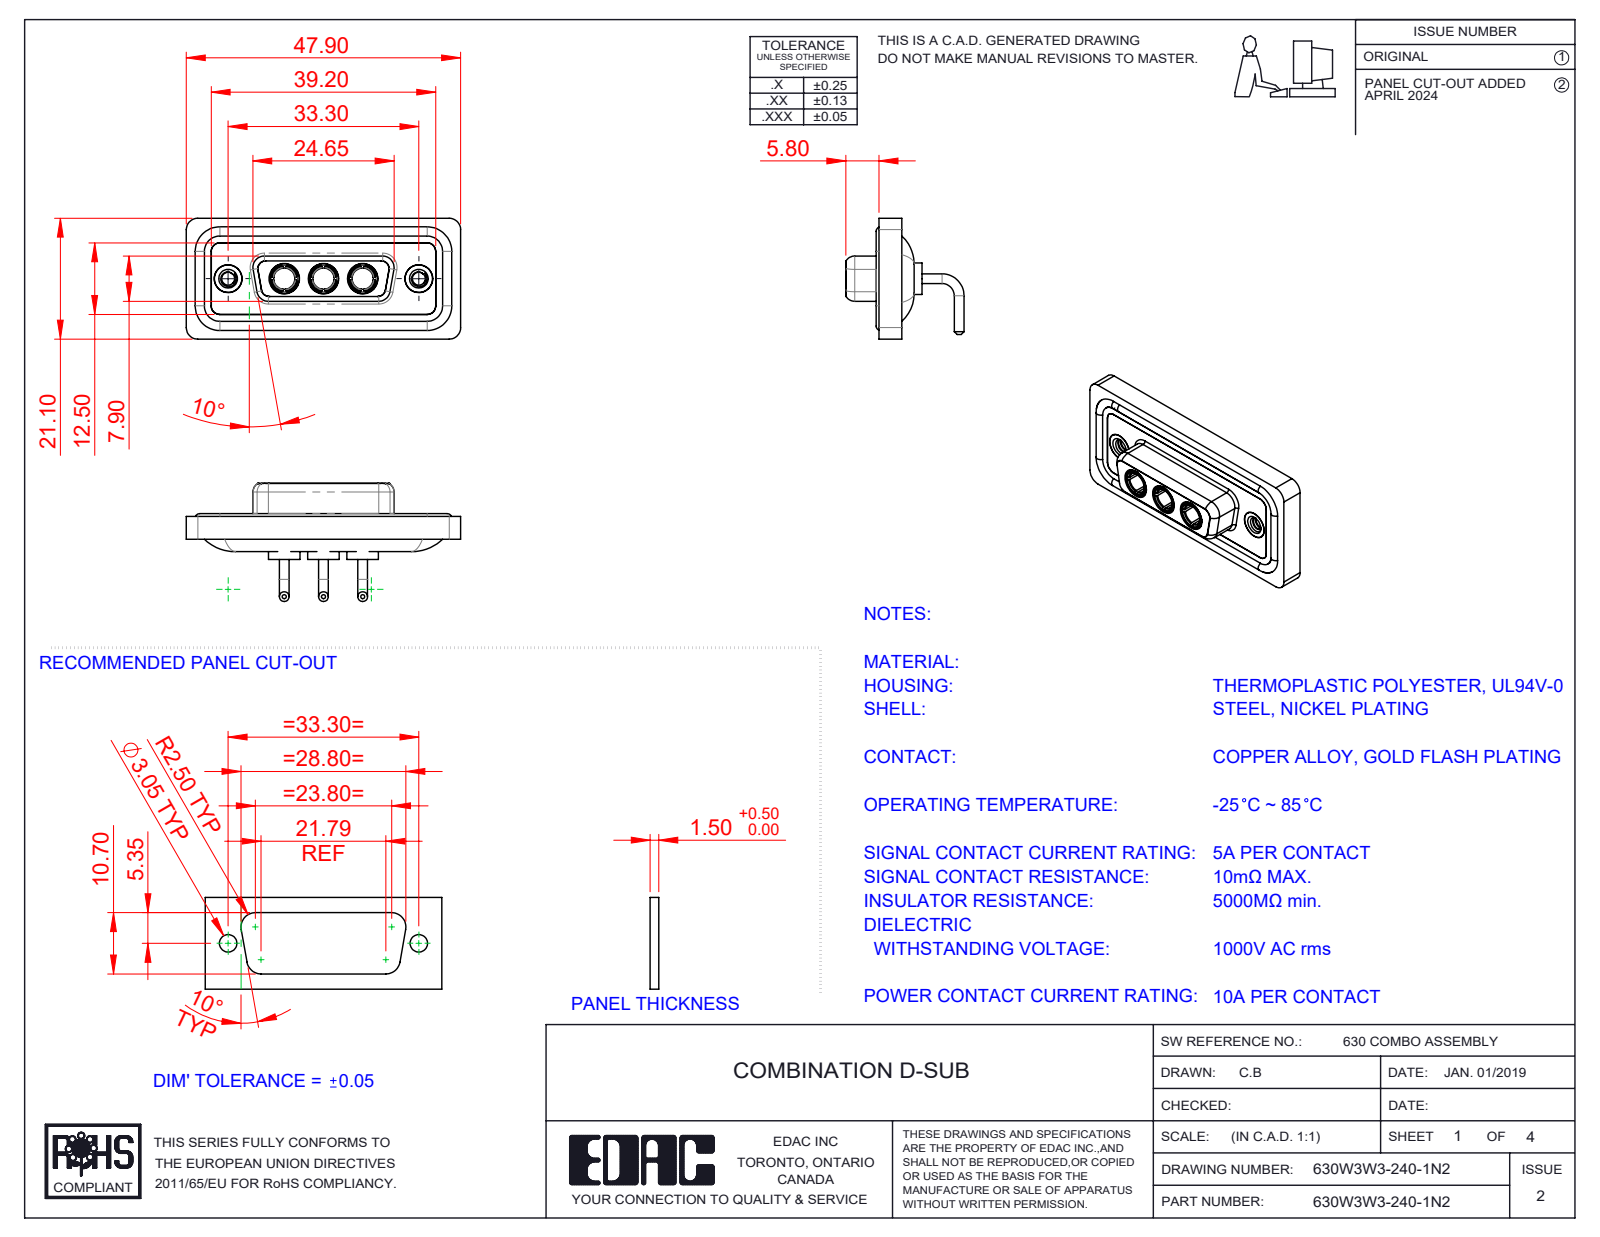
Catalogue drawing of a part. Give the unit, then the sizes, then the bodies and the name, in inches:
Units: inches
Overall size (bounding box): 1.886 × 0.831 × 0.813
Round holes (diameter × count): ⌀0.191 ×5, ⌀0.146 ×3, ⌀0.209 ×3, ⌀0.089 ×2, ⌀0.157 ×2, ⌀0.159 ×2, ⌀0.197 ×2
Round bosses / shafts (diameter × count): ⌀0.067 ×6, ⌀0.063 ×4, ⌀0.217 ×3, ⌀0.205 ×3, ⌀0.195 ×3, ⌀0.187 ×3, ⌀0.148 ×3, ⌀0.195 ×2
Partial cylindrical surfaces — rounded edges, fillets, slot ends (radius × count): R0.079 ×20, R0.059 ×18, R0.053 ×12, R0.063 ×8, R0.01 ×4, R0.02 ×4, R0.024 ×4, R0.026 ×4
Main face-to-face distances: 0.016, 0.071, 0.043, 0.063, 0.114, 0.098, 0.122, 0.146, 0.059, 0.161
Hole centre spacings: 0.27, 0.386, 0.656, 0.925, 0.539, 1.311
Volume: 0.367 in³ · Surface area: 15.22 in²
Bodies: 13 solids, 620 faces (192 planar, 263 cylindrical, 165 other)
Part name (STEP PRODUCT): 630Combo Housing_3W3; 630Combo Shell Rear_15 Contacts; 630Combo Waterproof Housing_15 Contacts; 630Combo Threaded Rivet_2 (+3 more)
STEP written by: SolidWorks 2023 (CONFIG_CONTROL_DESIGN)
